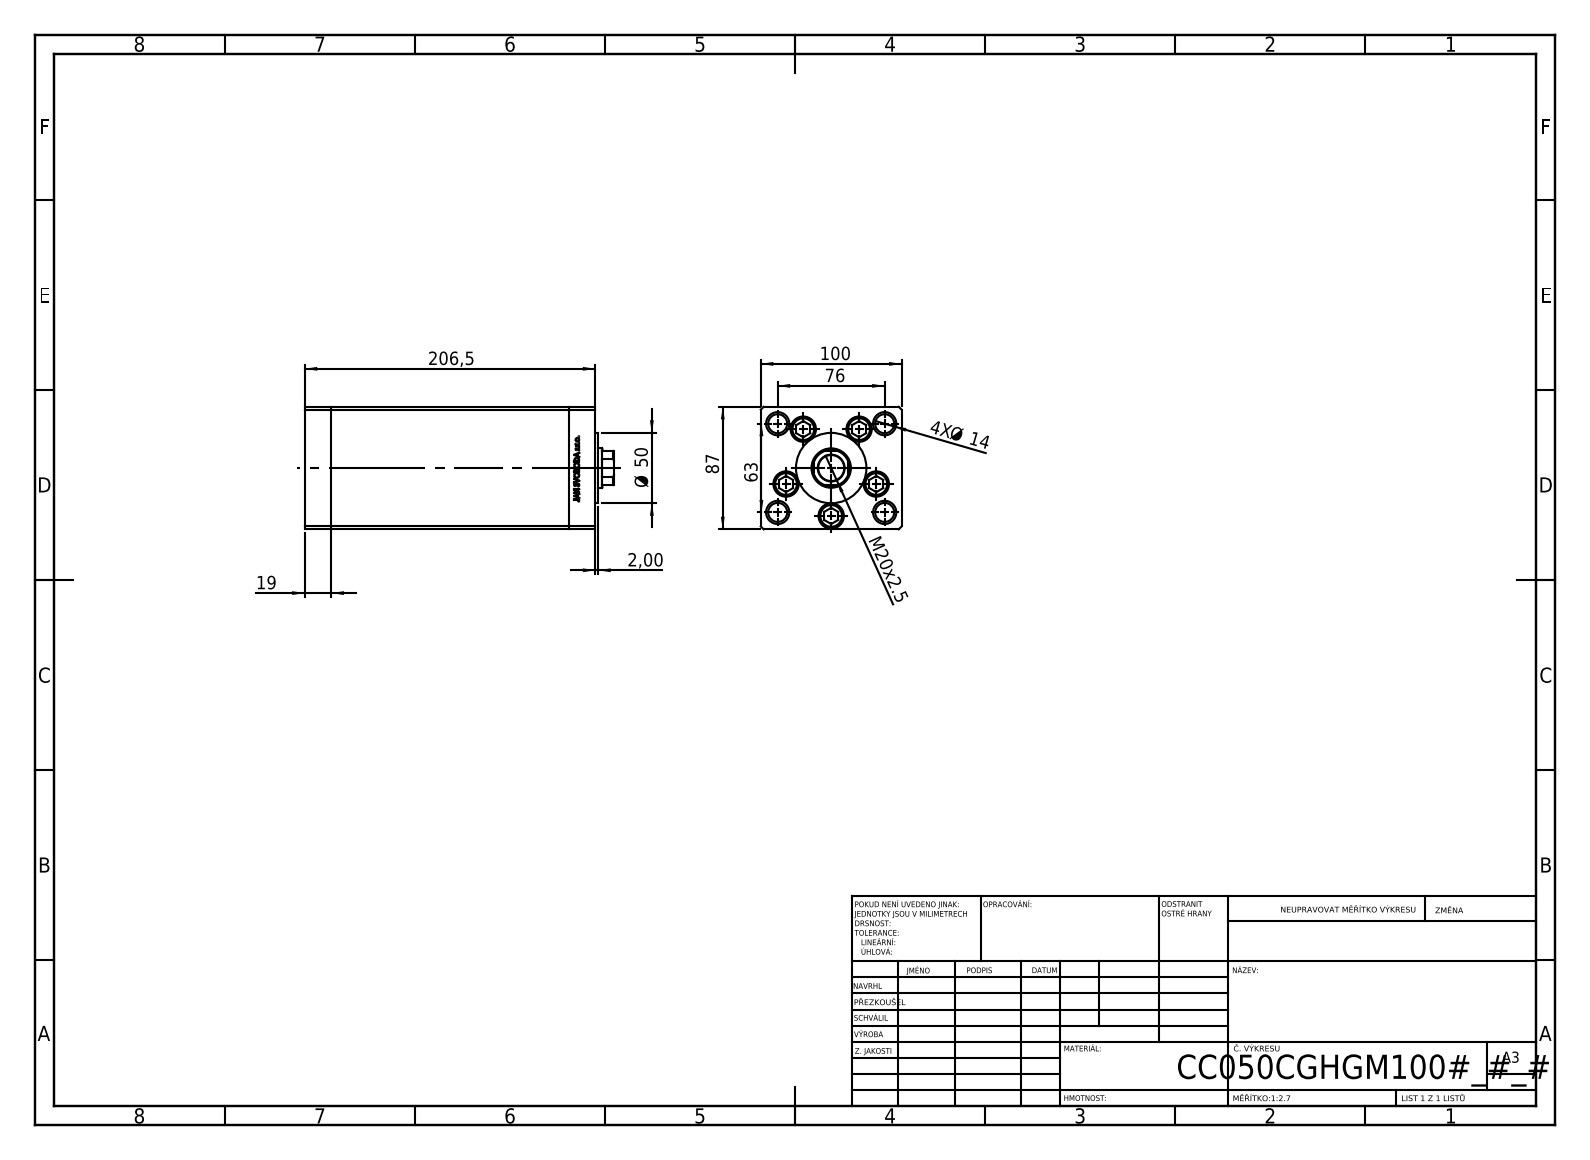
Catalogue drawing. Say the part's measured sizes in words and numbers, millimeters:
The part is named "ALLEN BOLT; V220C FRONT; V220C_C MIDDLE; V220C BACK_C (+1 more)". Its 3-D file was written by "SolidWorks 2019 (CONFIG_CONTROL_DESIGN)". It is 13 solids with 1186 faces: 548 planar, 176 cylindrical and 462 other. Overall it measures 219.5 by 100 by 87 millimeters. Its volume is 1 462 000 cubic millimeters and its surface area 247 386 square millimeters. Round holes: 9 of diameter 13.5, 5 of diameter 18, 4 of diameter 2, 4 of diameter 12, 4 of diameter 13.16, 4 of diameter 16.5, 1 of diameter 17, 1 of diameter 18.5, 1 of diameter 28. Round bosses or shafts: 5 of diameter 8, 4 of diameter 17, 1 of diameter 50. Partial cylindrical surfaces (rounded edges, fillets, slot ends): 2 of radius 0.93, 1 of radius 13.5. The main face-to-face distances are 100, 87, 19, 168.5, 187.5, 34.25, 206.5, 172.25, 153.25, 15.25. The hole center spacings are 34, 49.36, 18.59, 21.03, 38.08, 39.27, 40.83, 43.24.
